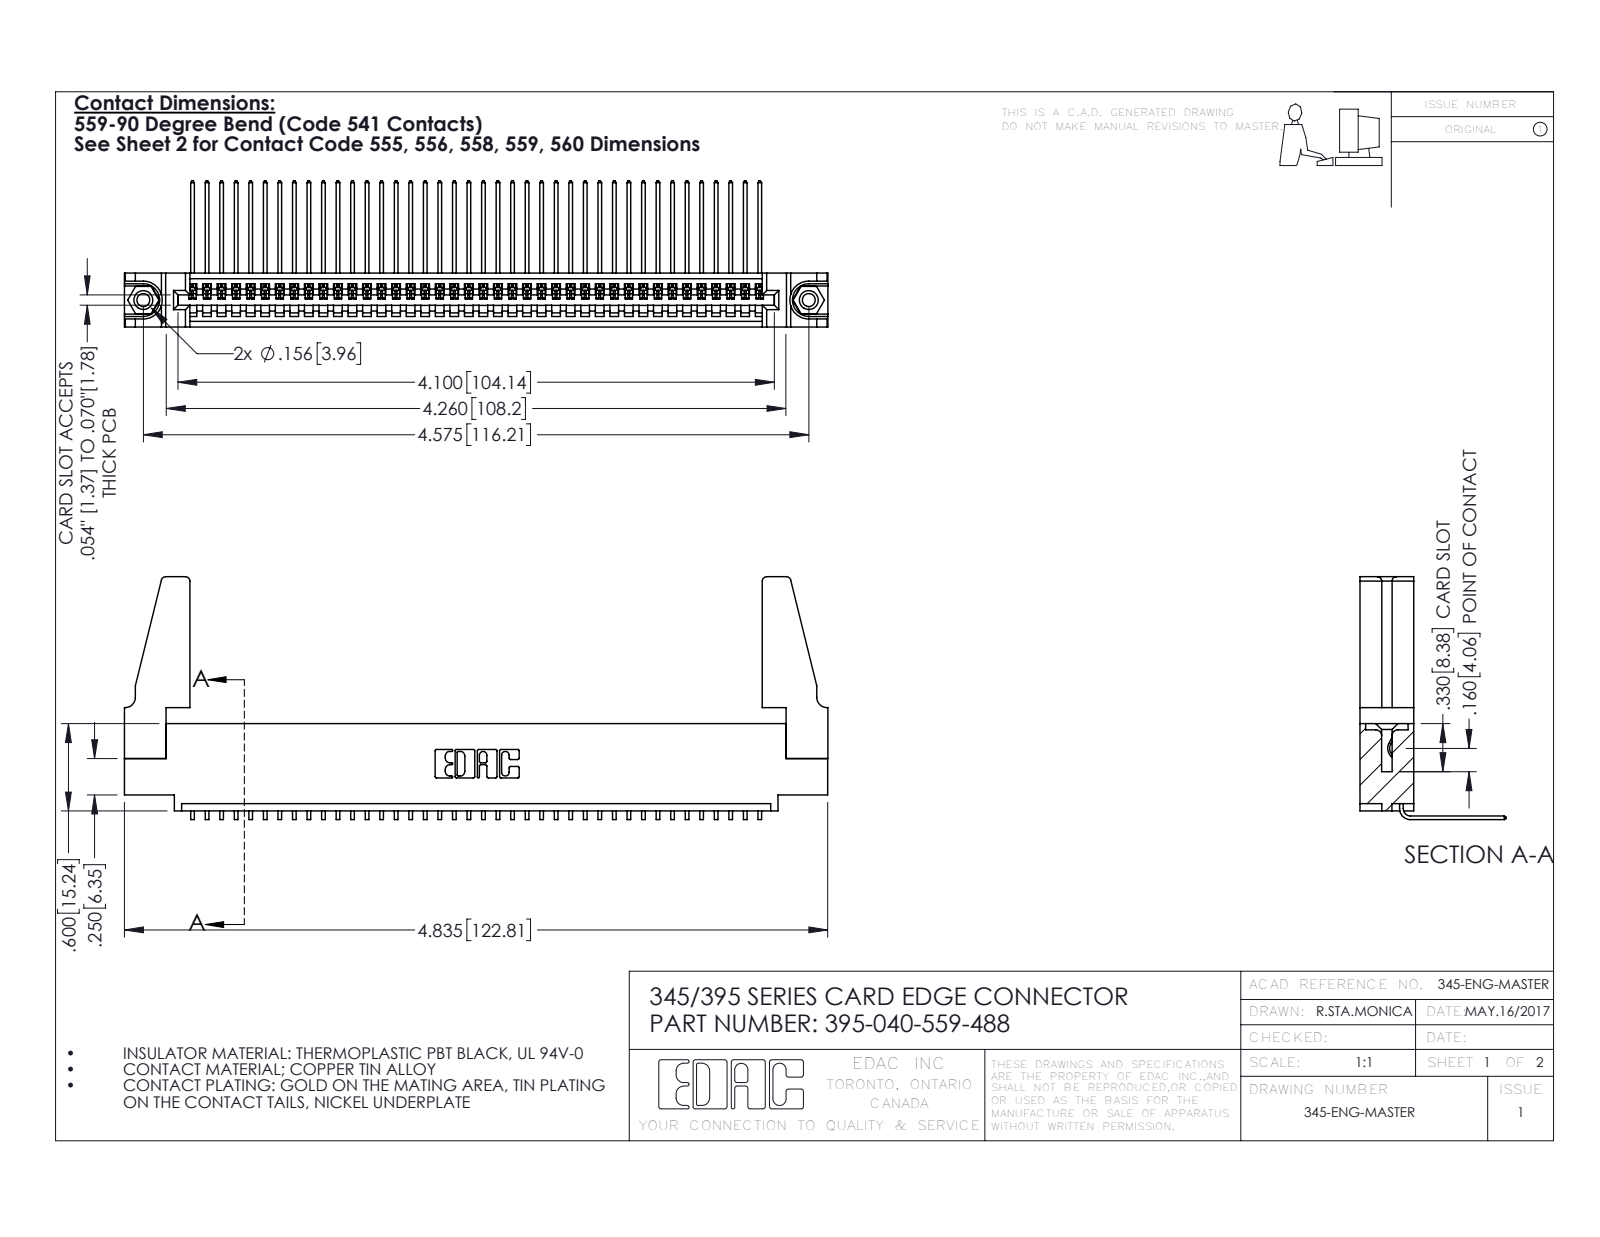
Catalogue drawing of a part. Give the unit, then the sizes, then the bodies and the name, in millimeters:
Units: millimetres
Overall size (bounding box): 122.8 × 42.4 × 25.5
Round holes (diameter × count): ⌀2.3 ×2, ⌀3.2 ×2, ⌀4 ×2, ⌀1.6 ×1
Round bosses / shafts (diameter × count): ⌀3.9 ×2
Partial cylindrical surfaces — rounded edges, fillets, slot ends (radius × count): R0.2 ×80, R0.3 ×22, R0.8 ×8, R0.2 ×6, R0.8 ×6, R0.7 ×3, R0.8 ×2, R1 ×2
Main face-to-face distances: 1.8, 9.4, 7.6, 5.1, 2.5, 6.9, 0.6, 5.7, 3.8, 1.8
Hole centre spacings: 6.9, 110.2, 116.2
Volume: 15 000 mm³ · Surface area: 19 530 mm²
Bodies: 45 solids, 2654 faces (1836 planar, 802 cylindrical, 16 other)
Part name (STEP PRODUCT): 395-040-559-488; 345-292-001_558 559 Tail - 1; 345 Part_0.110 Offset - 0.156 Dia-TH; 345-220-078_345-220-088 (+1 more)
STEP written by: SolidWorks 2016 (CONFIG_CONTROL_DESIGN)
